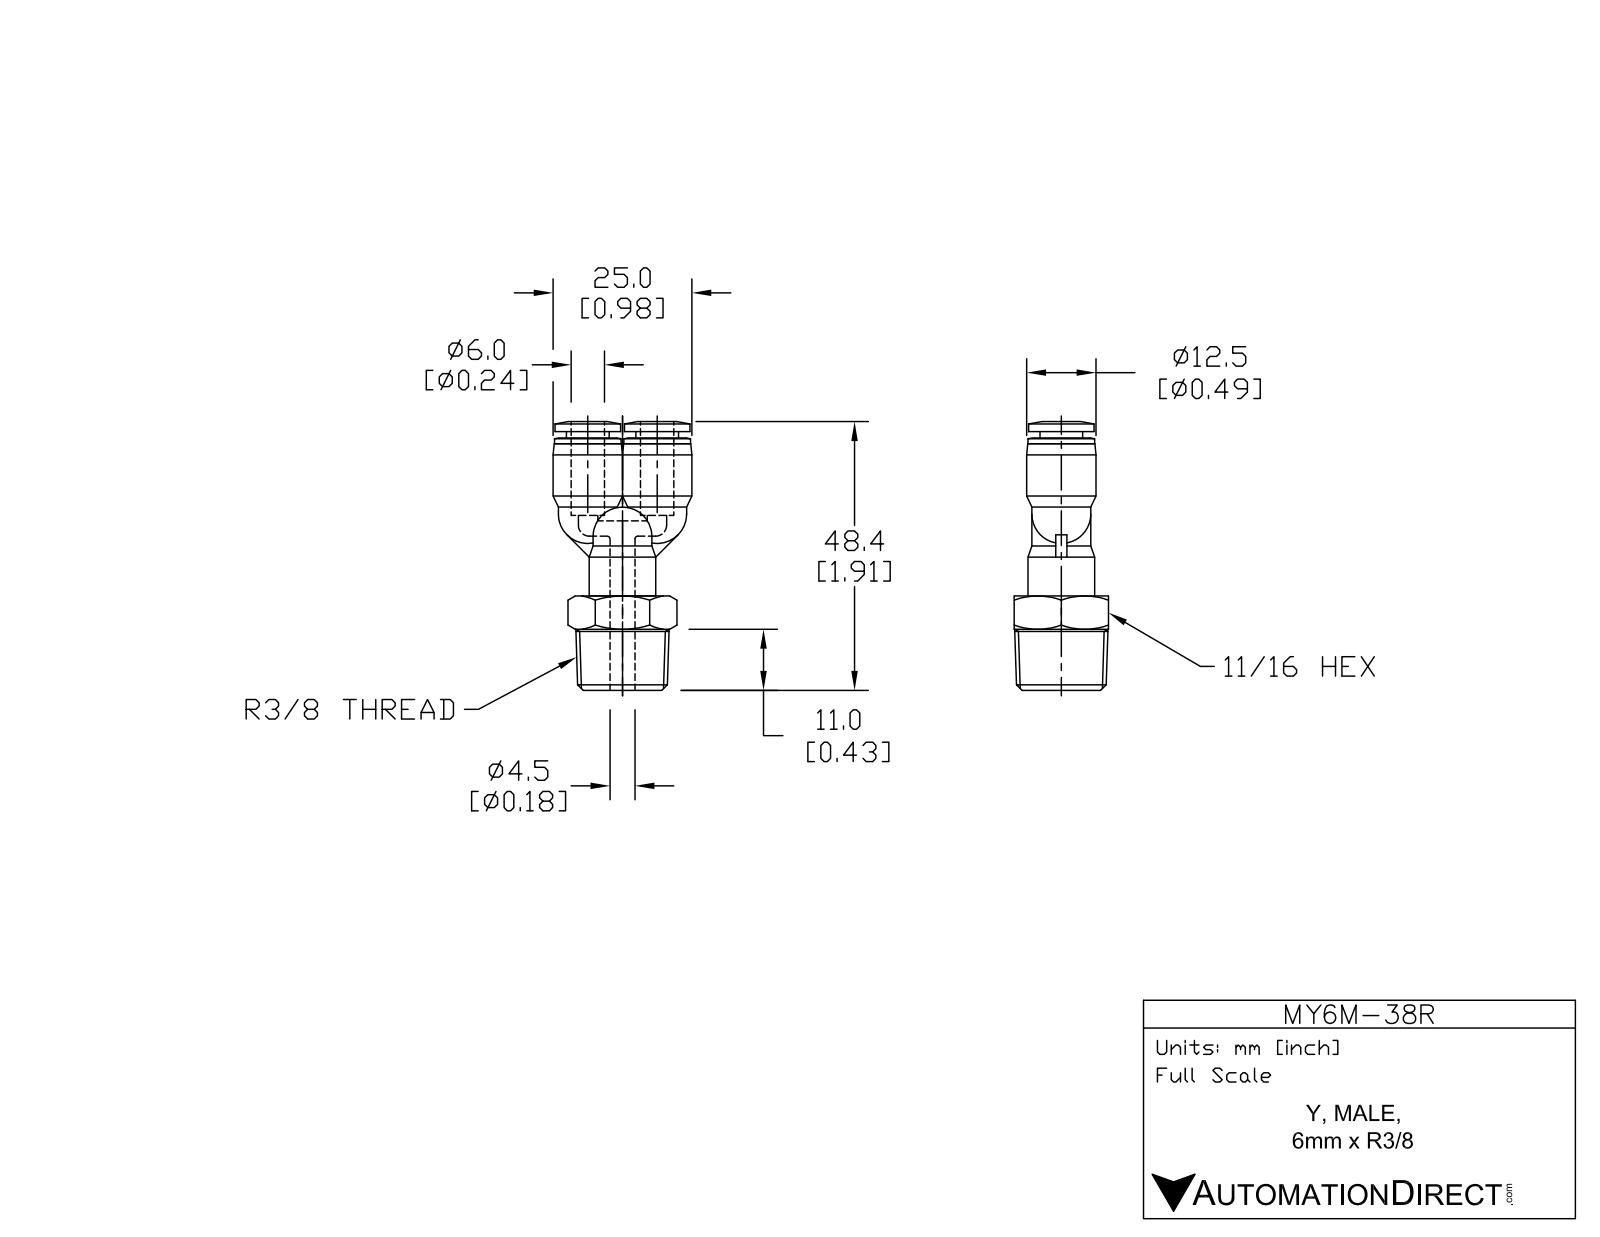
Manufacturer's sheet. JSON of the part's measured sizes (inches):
{"part_name": "MY6M-38R", "step_written_by": "SolidWorks 2018 (AUTOMOTIVE_DESIGN)", "units": "inches", "bodies": {"solids": 1, "faces": 106, "planar": 27, "cylindrical": 32, "other": 47}, "overall_size": [1.906, 0.984, 0.669], "volume_in3": 0.479, "surface_area_in2": 7.368, "round_holes": [[0.157, 4], [0.248, 2]], "round_bosses_or_shafts": [[0.472, 3], [0.417, 3], [0.492, 2], [0.465, 2], [0.303, 2]], "face_to_face_distances": [0.669, 1.835, 1.165, 1.789, 1.12, 0.045, 0.583, 1.252, 0.537, 0.295], "hole_center_spacings": [0.246, 0.492]}
